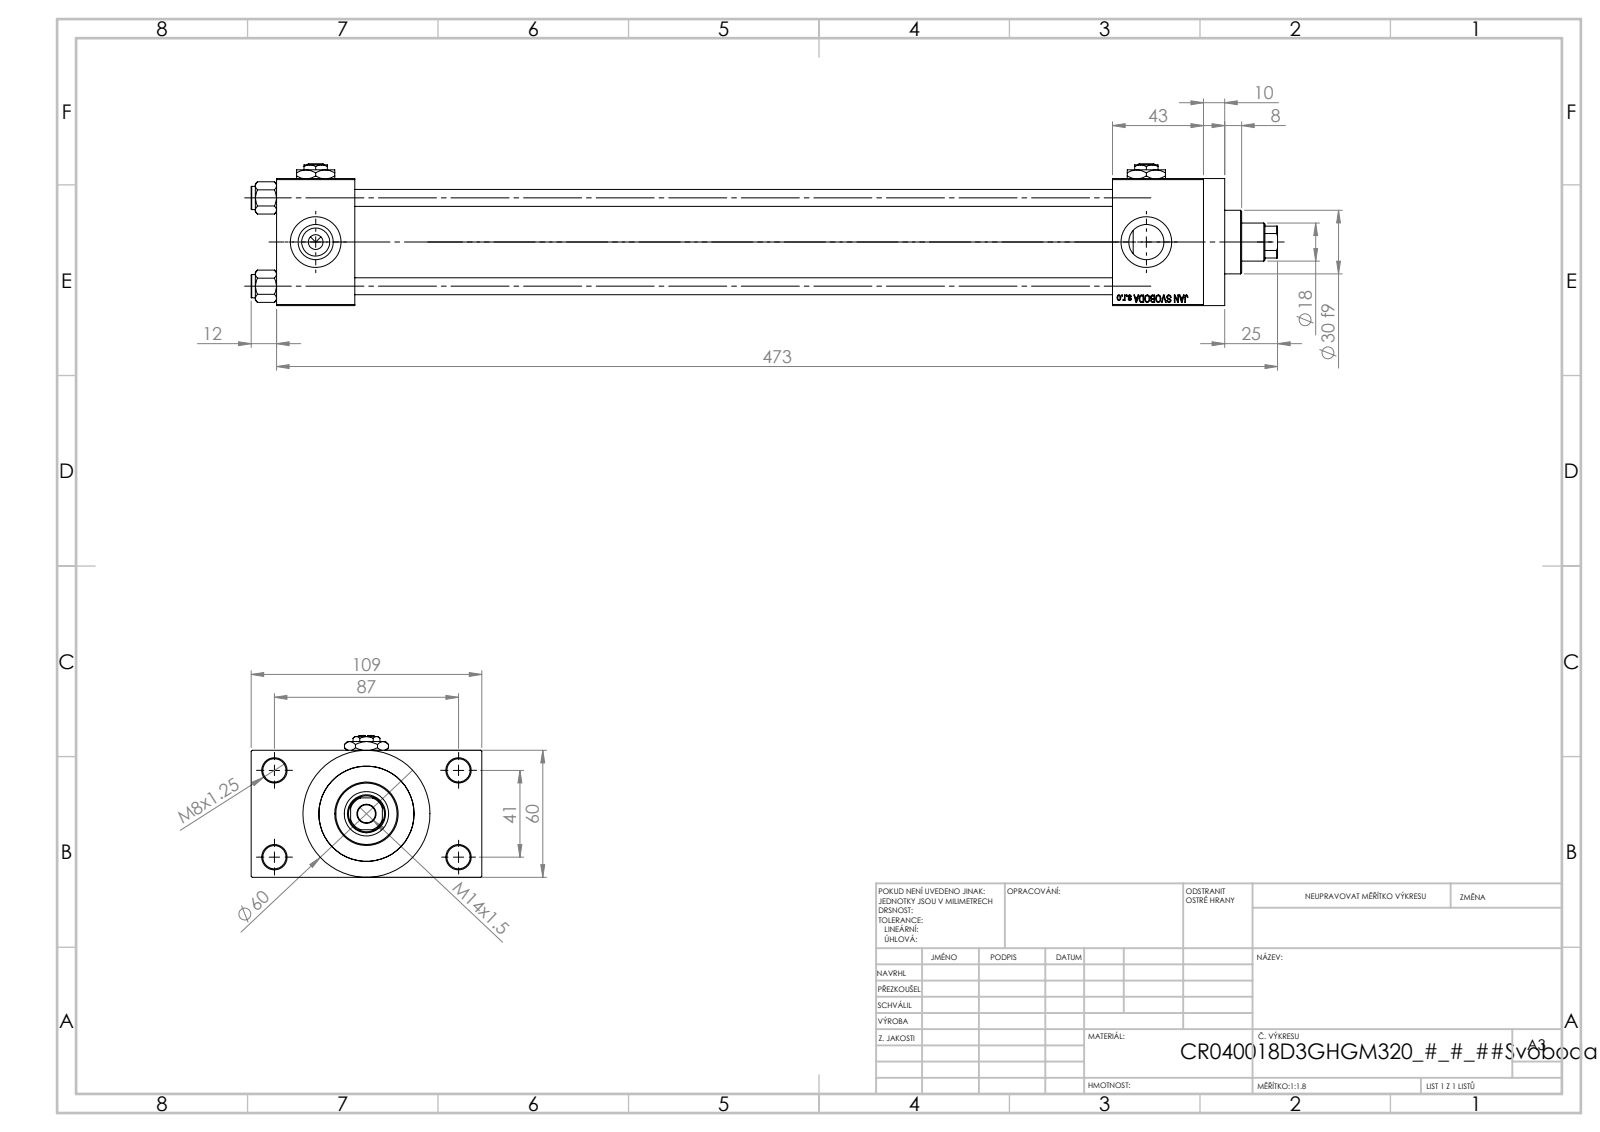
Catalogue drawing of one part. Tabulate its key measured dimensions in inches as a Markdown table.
| quantity | value |
| --- | --- |
| part name | V215_VC_A; NUT_M5_D; Zatka_pro_OIL_PORT; V215CR_VCP_D (+2 more) |
| STEP written by | SolidWorks 2019 (CONFIG_CONTROL_DESIGN) |
| units | inches |
| bodies | 13 solids, 1205 faces (546 planar, 99 cylindrical, 560 other) |
| overall size | 19.094 × 4.291 × 2.638 |
| volume | 46.9 in³ |
| surface area | 392.7 in² |
| round holes (diameter × count) | 0.315 × 4, 0.433 × 4, 0.656 × 4, 0.945 × 4, 0.276 × 3, 0.335 × 1, 0.709 × 1, 0.827 × 1, 1.22 × 1, 1.575 × 1, 1.772 × 1 |
| round bosses / shafts (diameter × count) | 0.433 × 4, 2.362 × 1, 1.811 × 1, 1.181 × 1 |
| partial cylindrical surfaces (radius × count) | 0.335 × 1 |
| main face-to-face distances | 2.362, 14.094, 0.965, 3.327, 1.457, 15.551, 1.693, 17.244, 15.787, 0.394 |
| hole center spacings | 0.892, 1.161, 1.642, 1.856, 1.893, 2.533, 3.011, 1.614 |
